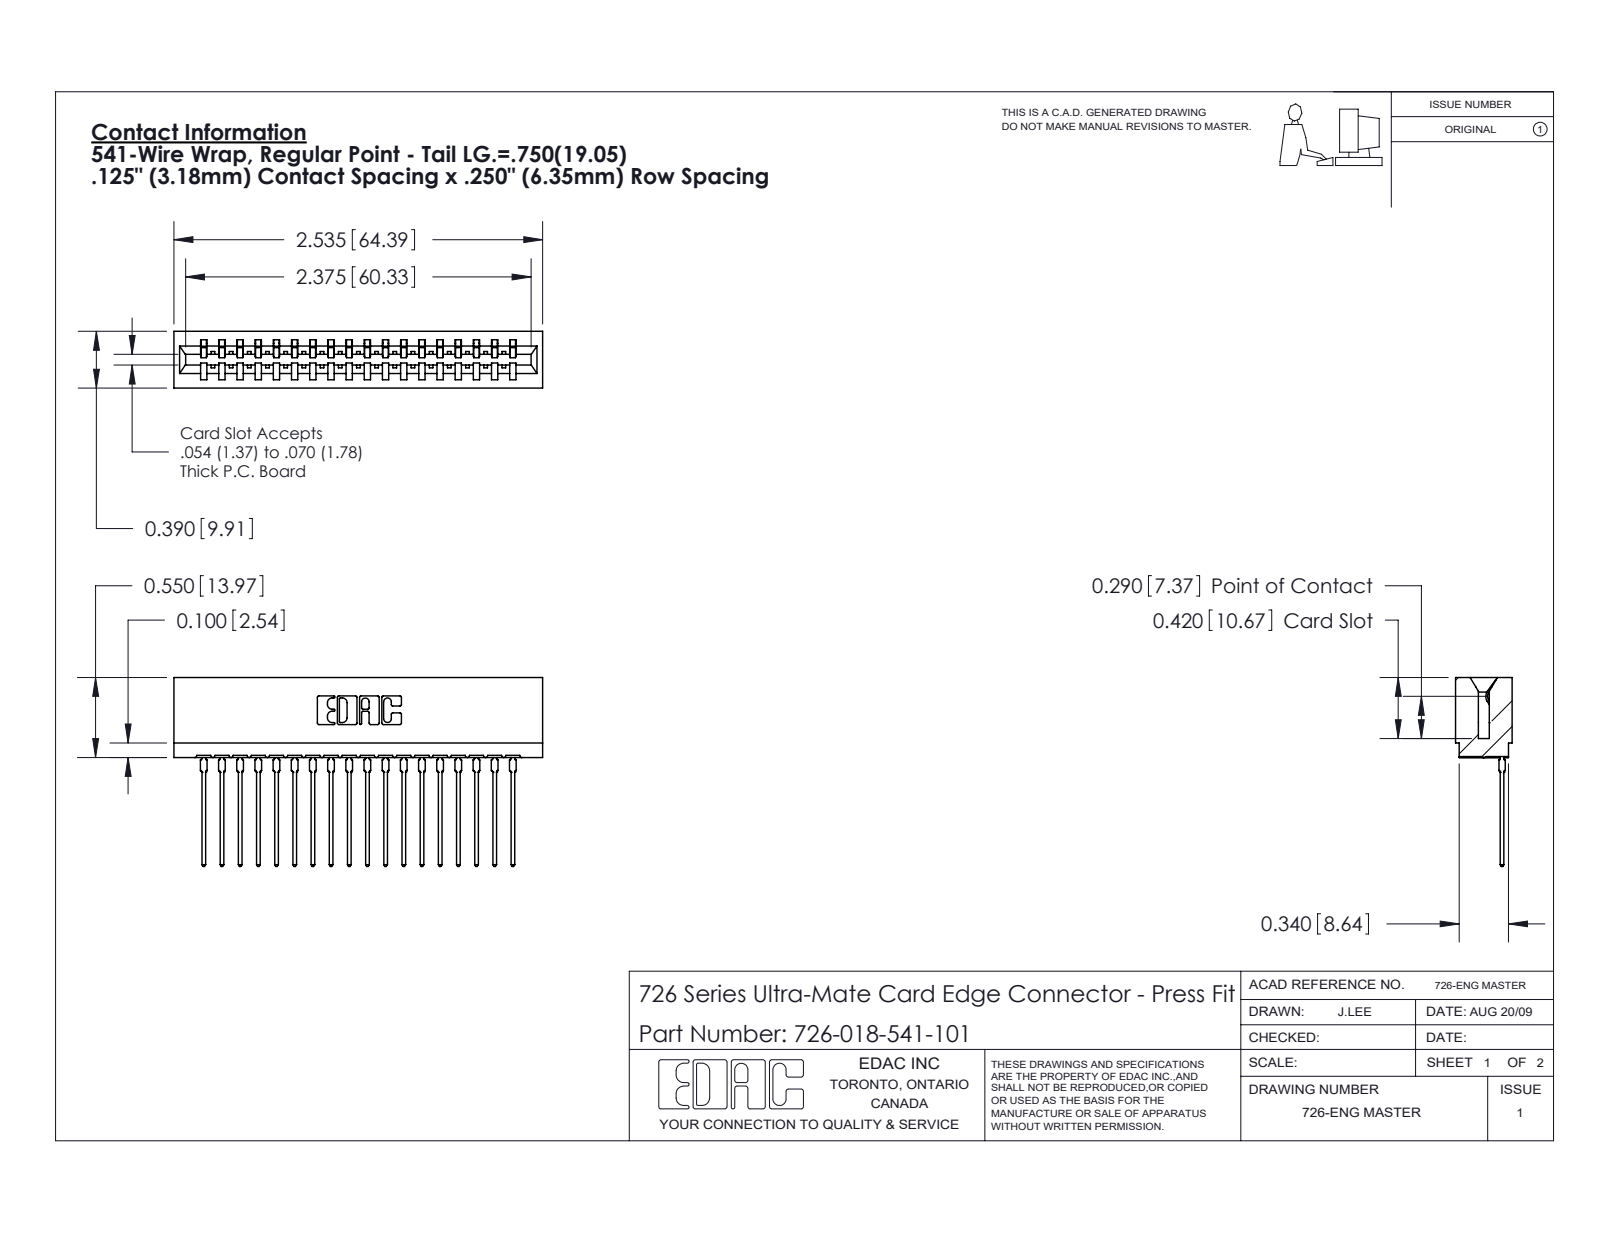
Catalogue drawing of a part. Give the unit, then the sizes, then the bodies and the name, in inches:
Units: inches
Overall size (bounding box): 2.535 × 1.299 × 0.39
Partial cylindrical surfaces — rounded edges, fillets, slot ends (radius × count): R0.021 ×36, R0.01 ×22, R0.015 ×19, R0.007 ×6, R0.031 ×6, R0.005 ×4, R0.011 ×4, R0.026 ×3
Main face-to-face distances: 0.057, 0.333, 0.25, 0.39, 0.025, 0.307, 0.083, 0.75, 0.5, 0.125
Volume: 0.364 in³ · Surface area: 14.25 in²
Bodies: 19 solids, 2041 faces (1189 planar, 384 cylindrical, 468 other)
Part name (STEP PRODUCT): 746-292-001_541; 726 Part_.515 Slot Depth - 01; 726-018-541-101
STEP written by: SolidWorks 2020 (CONFIG_CONTROL_DESIGN)
